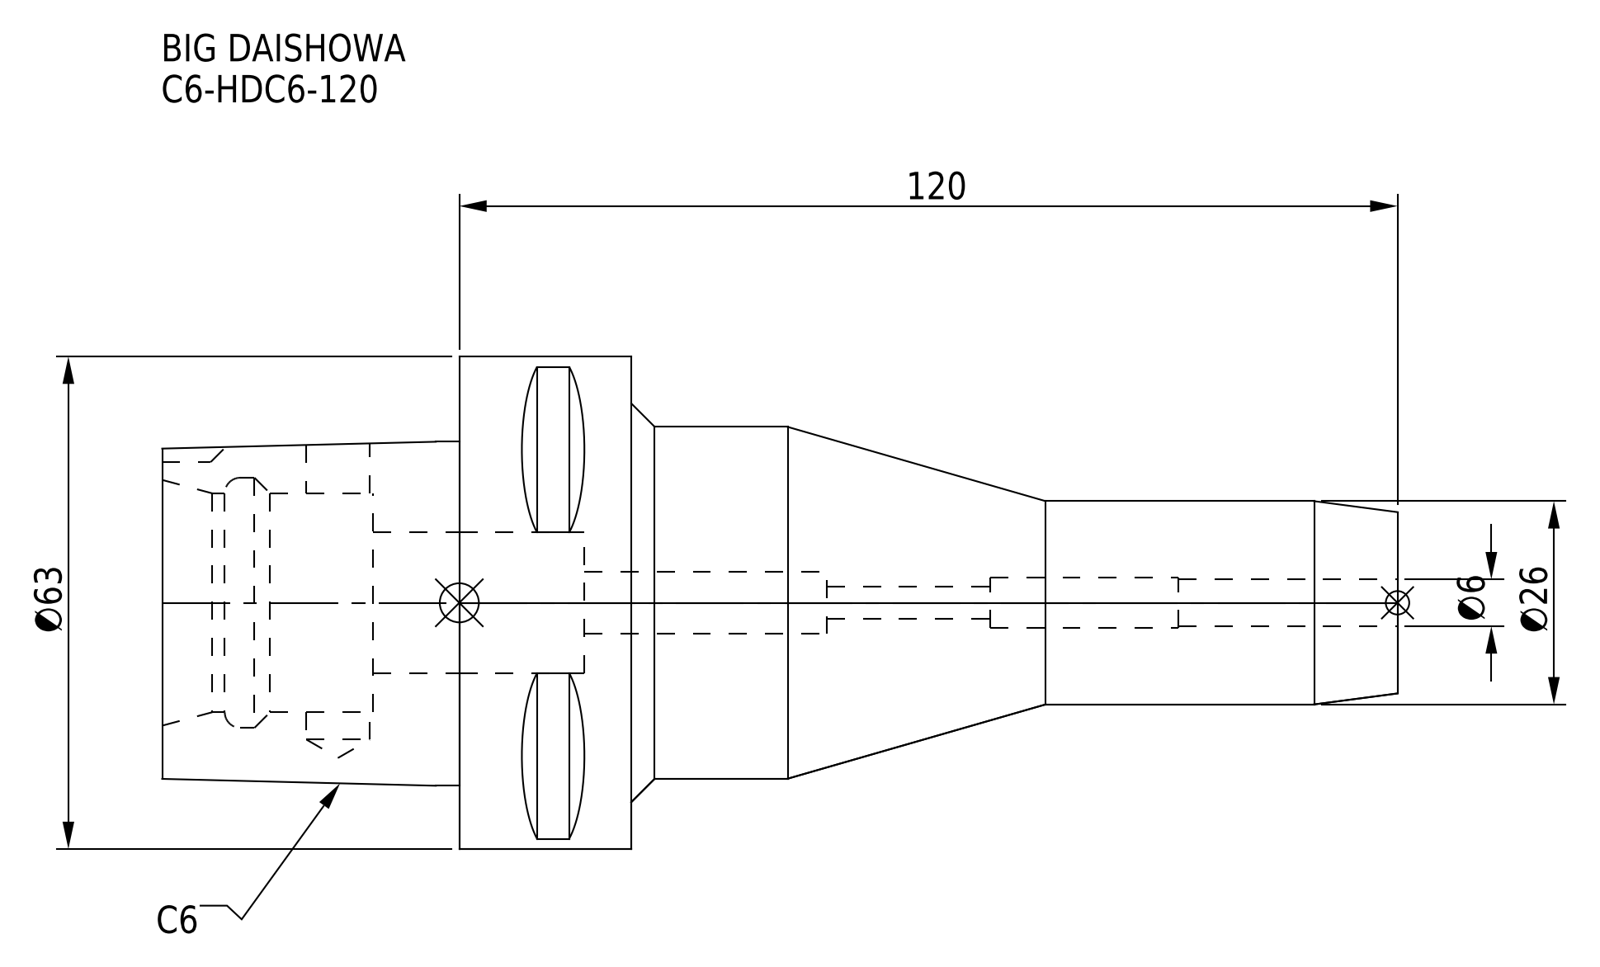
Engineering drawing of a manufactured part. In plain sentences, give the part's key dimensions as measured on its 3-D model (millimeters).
The part is named "C6-HDC6-120". Its 3-D file was written by "CREO PARAMETRIC BY PTC INC, 2016380 (AUTOMOTIVE_DESIGN)". It is 1 solid with 74 faces: 31 planar, 27 cylindrical and 16 other. Overall it measures 158 by 63 by 63 millimeters. Its volume is 182 363 cubic millimeters and its surface area 31 094 square millimeters. Round holes: 1 of diameter 4.2, 1 of diameter 6, 1 of diameter 6.5, 1 of diameter 8, 1 of diameter 8.1, 1 of diameter 18, 1 of diameter 28, 1 of diameter 32. Round bosses or shafts: 1 of diameter 63, 1 of diameter 45, 1 of diameter 26. Partial cylindrical surfaces (rounded edges, fillets, slot ends): 1 of radius 5. The main face-to-face distances are 22, 27, 60, 38, 98, 120, 158, 131, 33, 11.
